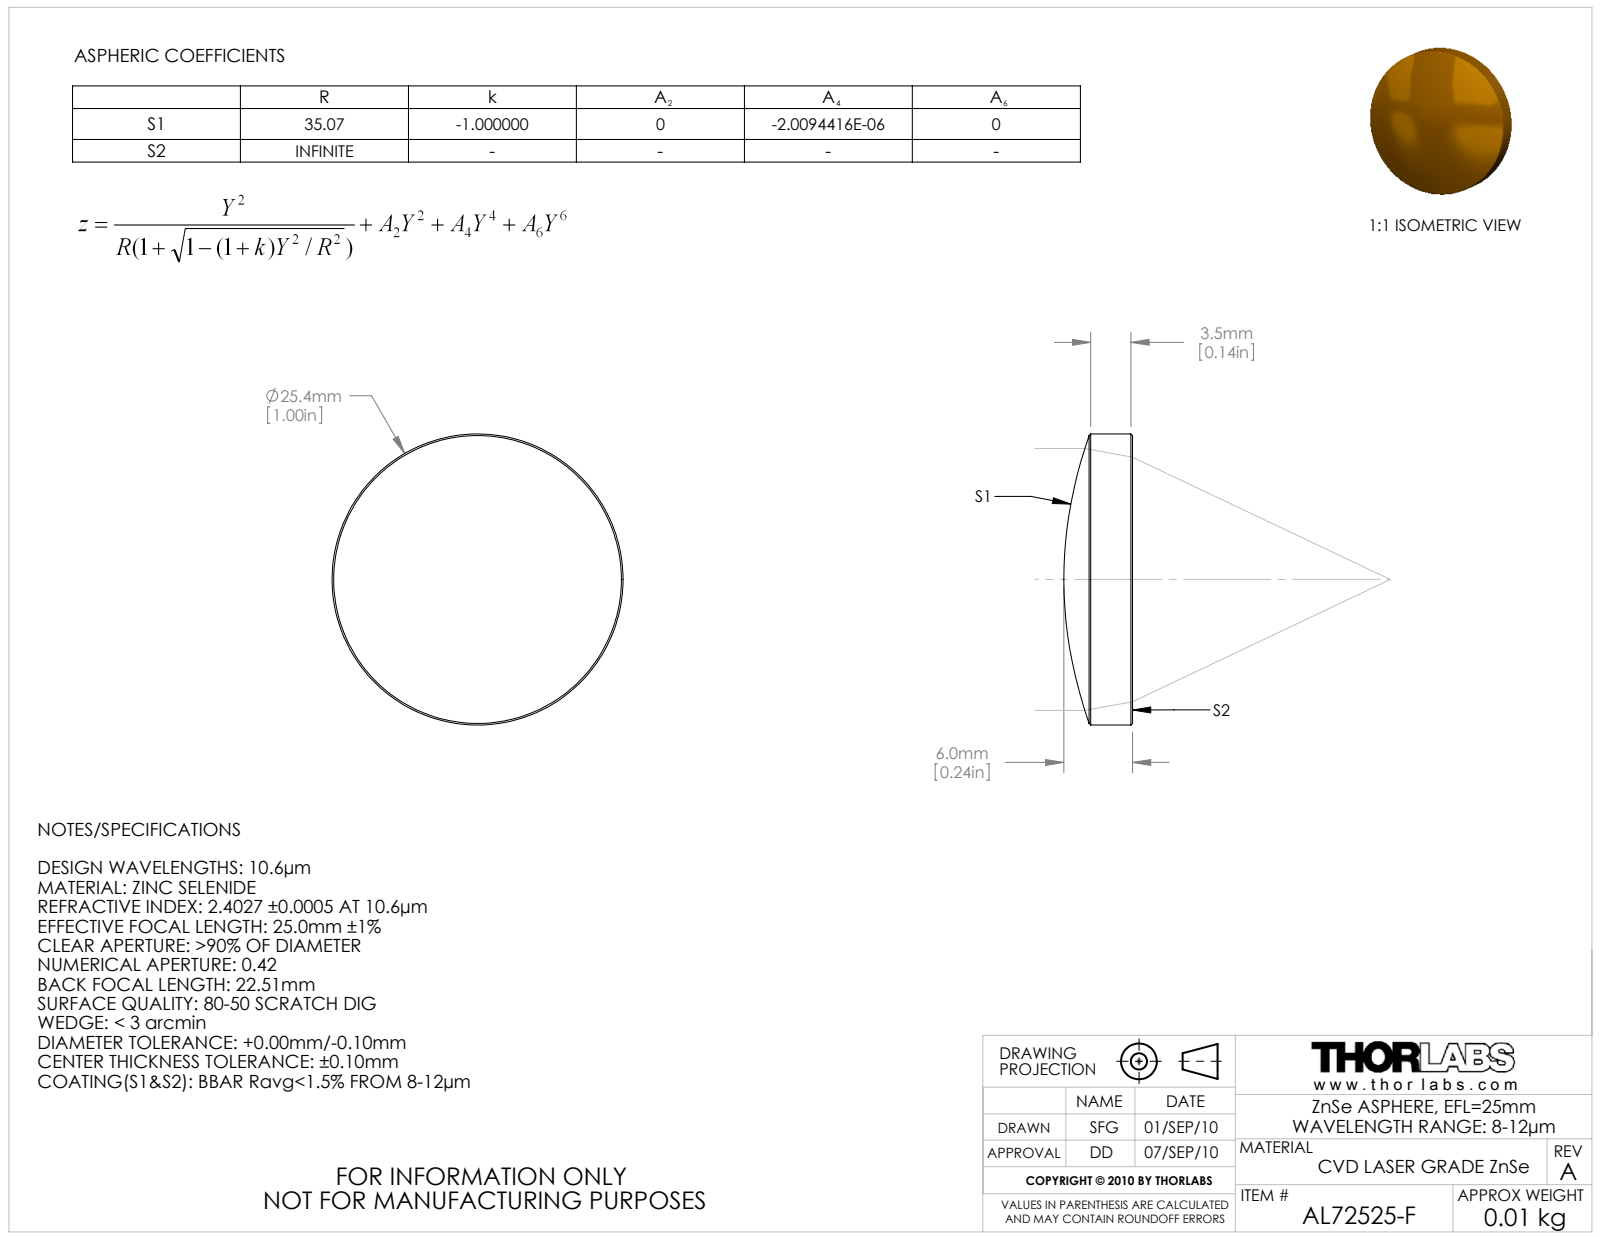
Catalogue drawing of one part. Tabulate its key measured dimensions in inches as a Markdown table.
| quantity | value |
| --- | --- |
| part name | 21487-E0W |
| STEP written by | SolidWorks 2009 (AUTOMOTIVE_DESIGN) |
| units | inches |
| bodies | 1 solid, 9 faces (1 planar, 2 cylindrical, 6 other) |
| overall size | 1 × 1 × 0.236 |
| volume | 0.15 in³ |
| surface area | 2.043 in² |
| round bosses / shafts (diameter × count) | 1 × 1 |
